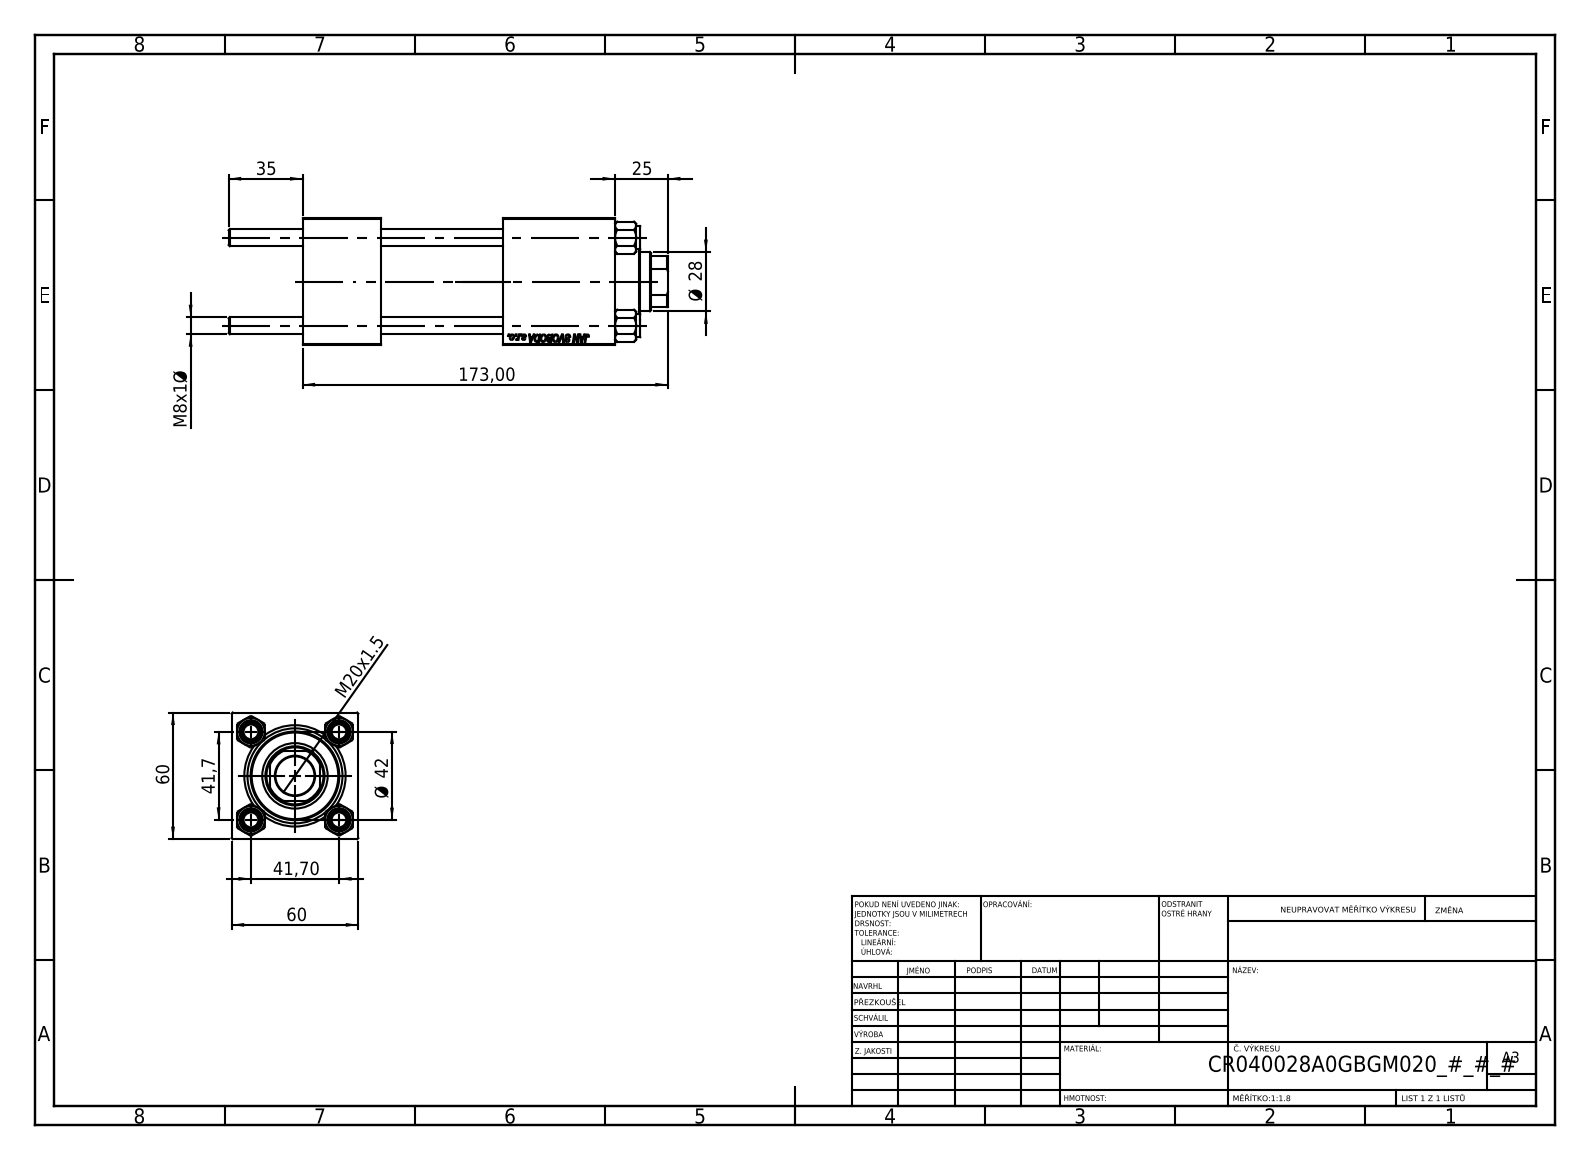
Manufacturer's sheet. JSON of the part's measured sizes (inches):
{"part_name": "V215CR_VCP; V215_VC_A; NUT_M5; V215CR_BODY_A (+1 more)", "step_written_by": "SolidWorks 2019 (CONFIG_CONTROL_DESIGN)", "units": "inches", "bodies": {"solids": 11, "faces": 1134, "planar": 520, "cylindrical": 78, "other": 536}, "overall_size": [8.189, 2.362, 2.362], "volume_in3": 26.58, "surface_area_in2": 186.2, "round_holes": [[0.315, 4], [0.276, 2], [0.656, 2], [0.945, 2], [0.728, 1], [1.102, 1], [1.22, 1], [1.575, 1], [1.772, 1]], "round_bosses_or_shafts": [[0.433, 4], [1.811, 1], [1.654, 1]], "partial_cylinders_radius": [[0.531, 1]], "face_to_face_distances": [2.362, 1.457, 2.283, 3.74, 2.087, 5.827, 4.37, 4.697, 3.24, 0.957], "hole_center_spacings": [1.161, 1.642, 2.322, 3.642]}
